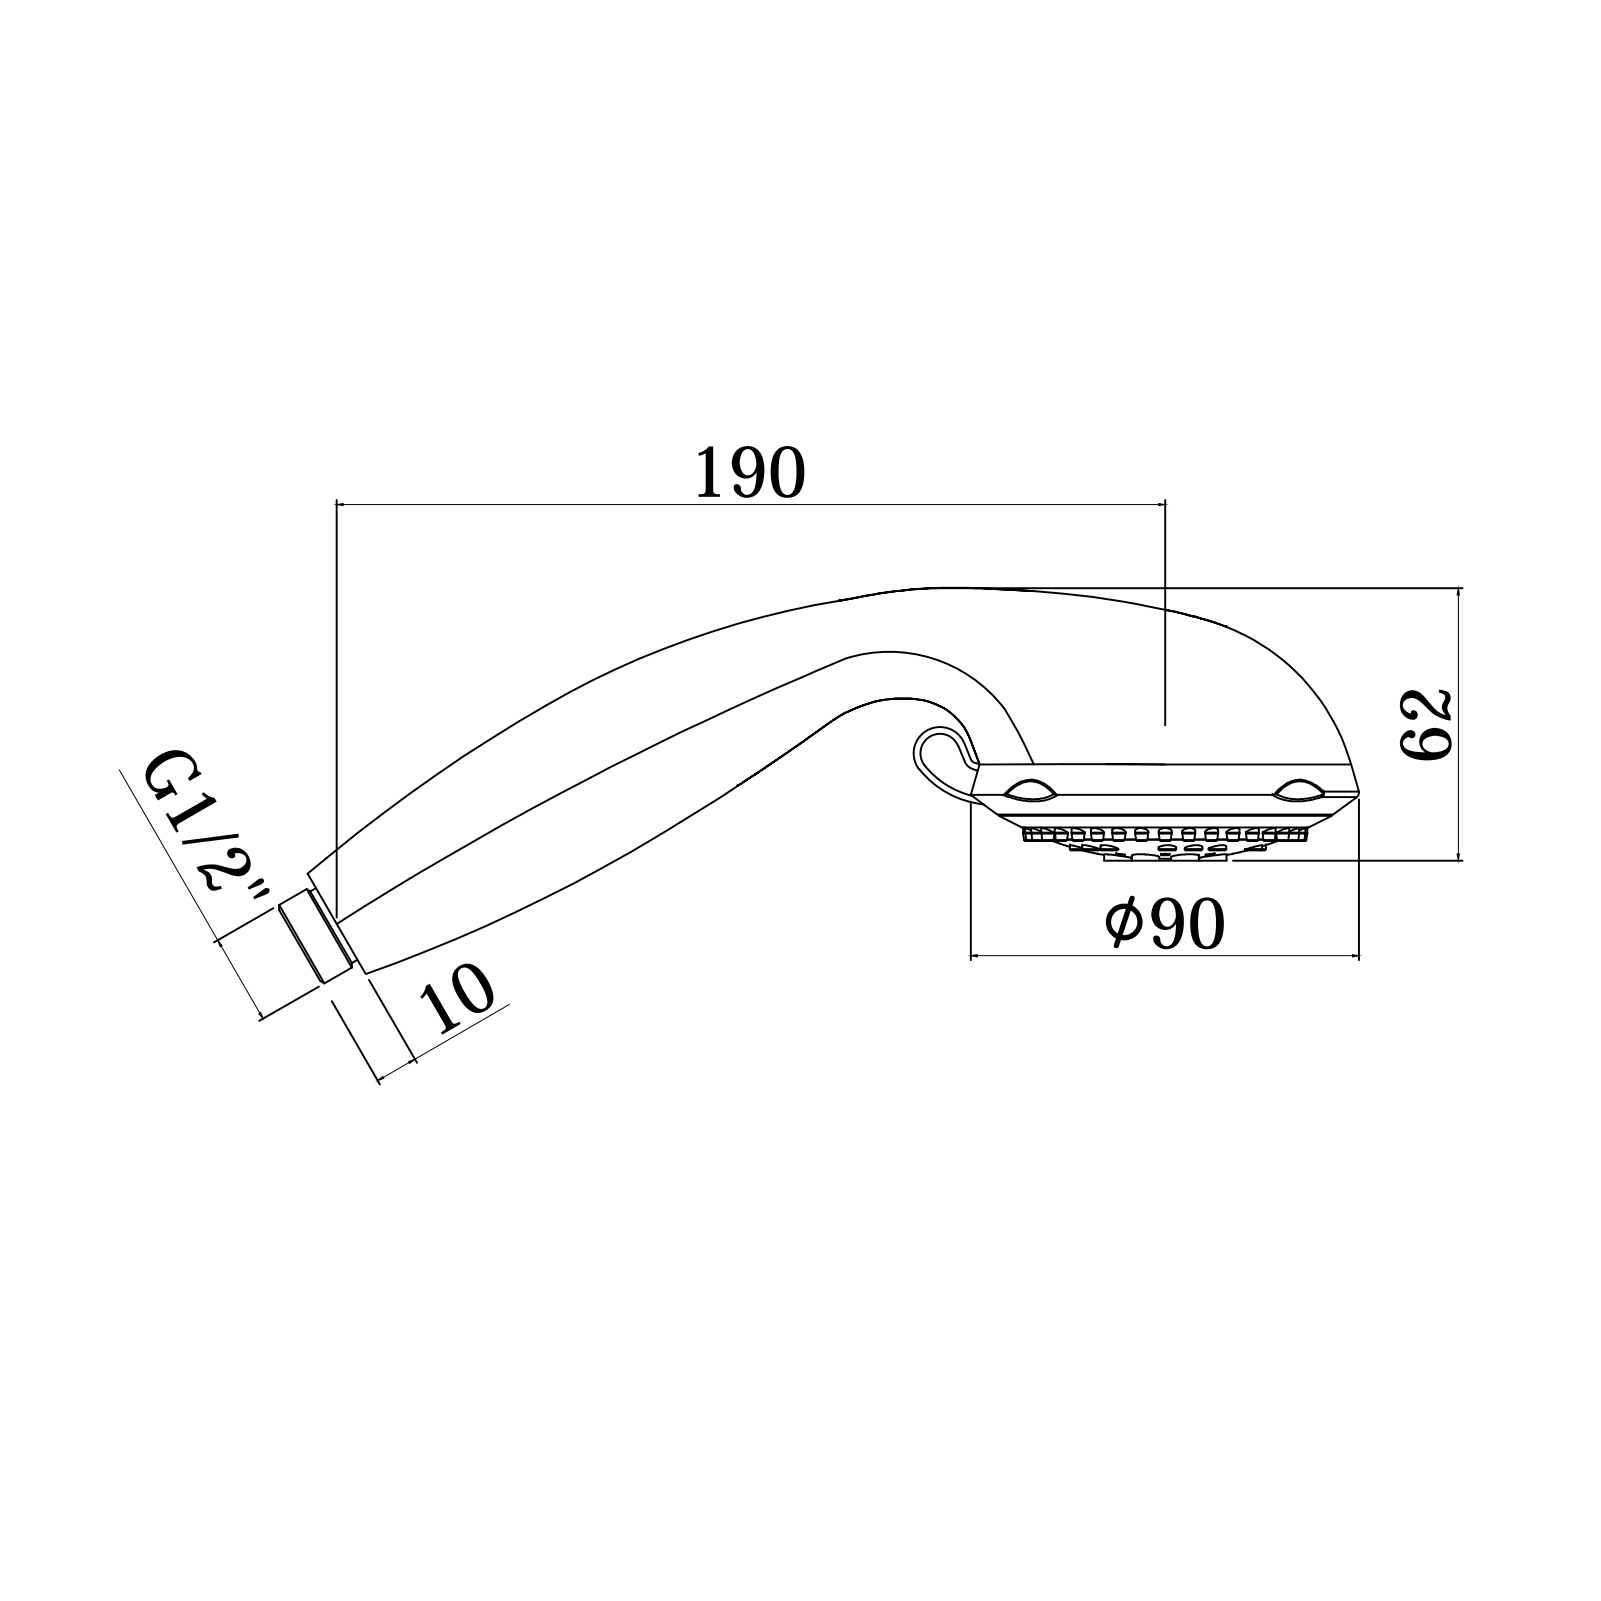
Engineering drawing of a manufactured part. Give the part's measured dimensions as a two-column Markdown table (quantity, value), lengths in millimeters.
| quantity | value |
| --- | --- |
| part name | ZDOC077CR |
| STEP written by | CREO PARAMETRIC BY PTC INC, 2020044 (CONFIG_CONTROL_DESIGN) |
| units | millimeters |
| bodies | 3 solids, 671 faces (83 planar, 226 cylindrical, 362 other) |
| overall size | 246.98 × 90.47 × 89 |
| volume | 376 053 mm³ |
| surface area | 48 985 mm² |
| round holes (diameter × count) | 0.8 × 36, 1.5 × 15, 2 × 8, 4 × 8, 11 × 1, 13 × 1, 14 × 1, 53.5 × 1 |
| round bosses / shafts (diameter × count) | 6.3 × 8, 52 × 1, 20.7 × 1, 18.94 × 1 |
| partial cylindrical surfaces (radius × count) | 1.5 × 41, 2 × 15, 46.34 × 4, 6 × 1, 21.63 × 1 |
| main face-to-face distances | 10.25, 10.5, 5.25, 5.75, 5, 9.79, 4.5, 0.75, 6, 2.3 |
| hole center spacings | 14.76, 21.88, 14.5, 21, 5.78, 5.79, 11.1, 11.76 |
